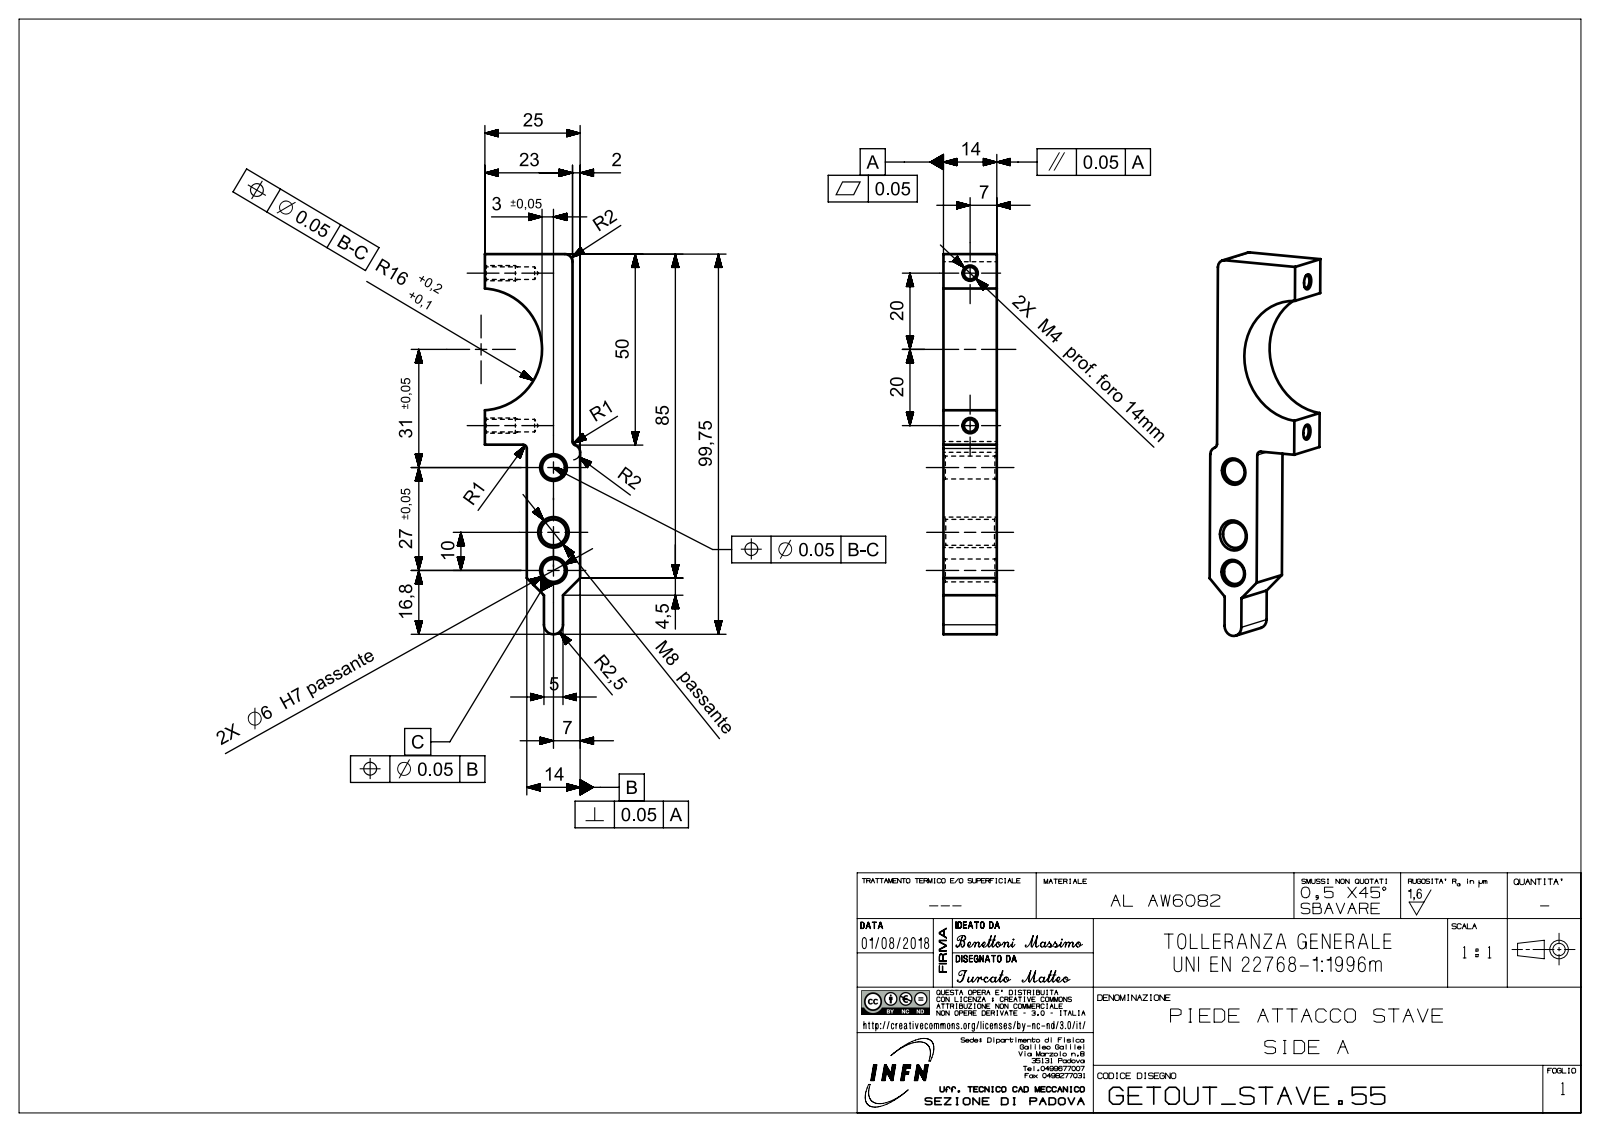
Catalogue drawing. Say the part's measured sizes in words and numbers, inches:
The part is named "bezA730AE56ccuu". Its 3-D file was written by "SIEMENS PLM Software NX 12.0 (AUTOMOTIVE_DESIGN)". It is 1 solid with 34 faces: 13 planar, 11 cylindrical and 10 other. Overall it measures 3.927 by 0.984 by 0.551 inches. Its volume is 1.067 cubic inches and its surface area 11.13 square inches. Round holes: 2 of diameter 0.13, 2 of diameter 0.236, 1 of diameter 0.268. Partial cylindrical surfaces (rounded edges, fillets, slot ends): 2 of radius 0.039, 2 of radius 0.079, 1 of radius 0.098, 1 of radius 0.63. The main face-to-face distances are 0.551, 0.472, 0.079, 0.984, 0.906, 0.433, 0.177, 0.374, 1.969, 0.098. The hole center spacings are 0.394, 0.669, 1.063, 1.575.
